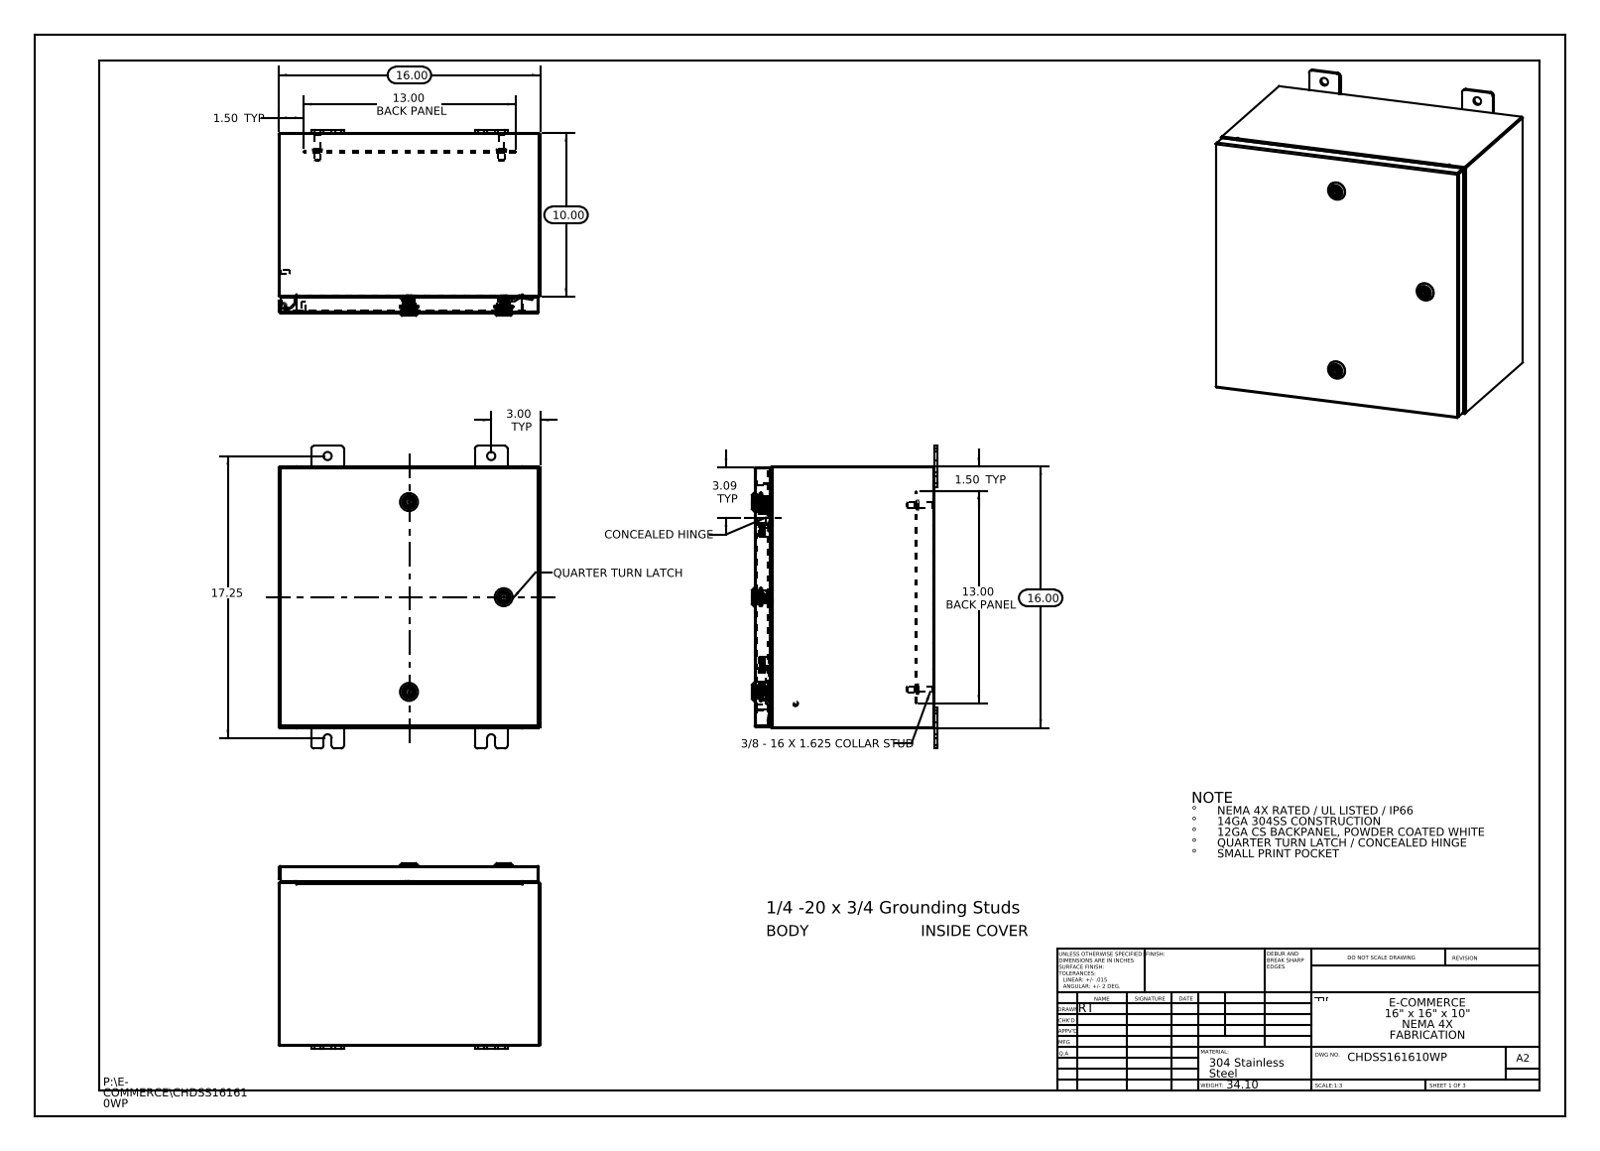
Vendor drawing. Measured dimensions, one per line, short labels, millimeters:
name: CHDSS161610WP Mounting Feet; Housing-211301-IB-Industrilas_Housing-211301-IB-Industrilas; HW-CLH-E5-8004_Cam-232112-U-Industrilas; CHDSS161610WP Backpanel (+8 more)
written by: SolidWorks 2013 (CONFIG_CONTROL_DESIGN)
unit: mm
bodies: 37 solids, 2966 faces (938 planar, 930 cylindrical, 1098 other)
size: 469.9 × 406.4 × 288.4
volume: 1 993 000 mm³; area: 1 994 000 mm²
holes: 8× ⌀12.7, 4× ⌀3.5, 3× ⌀5, 3× ⌀10, 3× ⌀10.2, 3× ⌀16, 3× ⌀20, 1× ⌀5.4
bosses: 5× ⌀6, 4× ⌀15.9, 4× ⌀9.5, 4× ⌀8.4, 3× ⌀28, 3× ⌀19.8, 3× ⌀15.9, 3× ⌀15.5
rounds: 99× R0.2, 99× R3, 36× R0.7, 24× R4.8, 18× R0.3, 18× R2.2, 12× R0.5, 12× R5
face distances: 1.9, 404.5, 1.9, 402.6, 406.4, 279.7, 277.7, 277.8, 275.9, 25.4
hole spacings: 17.5, 47.2, 77.9, 142.9, 246, 254, 285.8, 285.8
